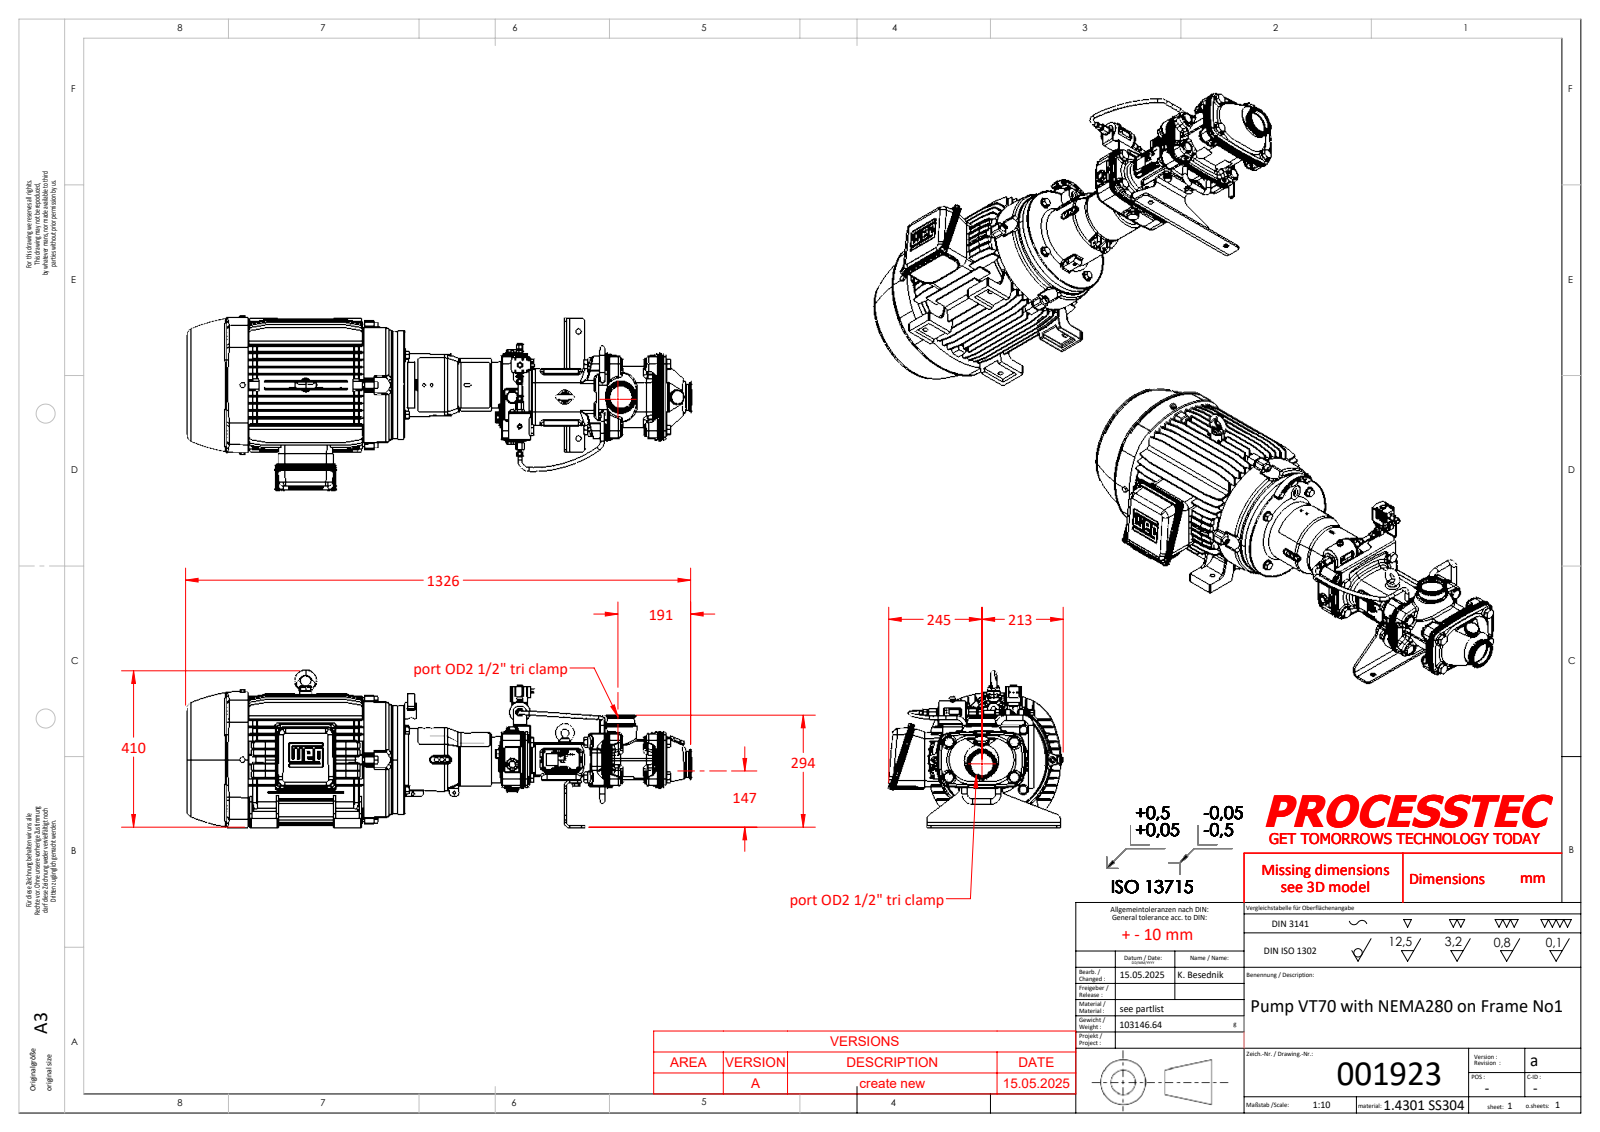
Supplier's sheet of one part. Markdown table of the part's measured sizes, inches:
| quantity | value |
| --- | --- |
| part name | 001257; 001833; 001588_console_off; 001321 (+8 more) |
| STEP written by | SolidWorks 2023 (AUTOMOTIVE_DESIGN) |
| units | inches |
| bodies | 85 solids, 11368 faces (5002 planar, 2030 cylindrical, 4336 other) |
| overall size | 52.197 × 18.034 × 16.154 |
| volume | 3 645 in³ |
| surface area | 5 234 in² |
| round holes (diameter × count) | 0.315 × 15, 0.335 × 10, 0.551 × 10, 0.413 × 7, 0.098 × 5, 0.591 × 5, 0.689 × 5, 0.134 × 4, 0.268 × 4, 0.531 × 4, 0.531 × 4, 0.669 × 4 |
| round bosses / shafts (diameter × count) | 0.236 × 19, 0.63 × 10, 0.394 × 10, 0.945 × 8, 0.52 × 6, 0.315 × 6, 1.102 × 5, 0.472 × 5 |
| partial cylindrical surfaces (radius × count) | 0.079 × 144, 0.157 × 85, 0.118 × 76, 0.02 × 60, 0.315 × 56, 0.197 × 38, 0.055 × 16, 0.591 × 16 |
| main face-to-face distances | 12.717, 0.735, 7.448, 1.3, 0.565, 0.206, 26.882, 14.165, 6.694, 6.713 |
| hole center spacings | 6.252, 1.614, 5.732, 0.159, 0.889, 1.772, 2.335, 3.071 |
